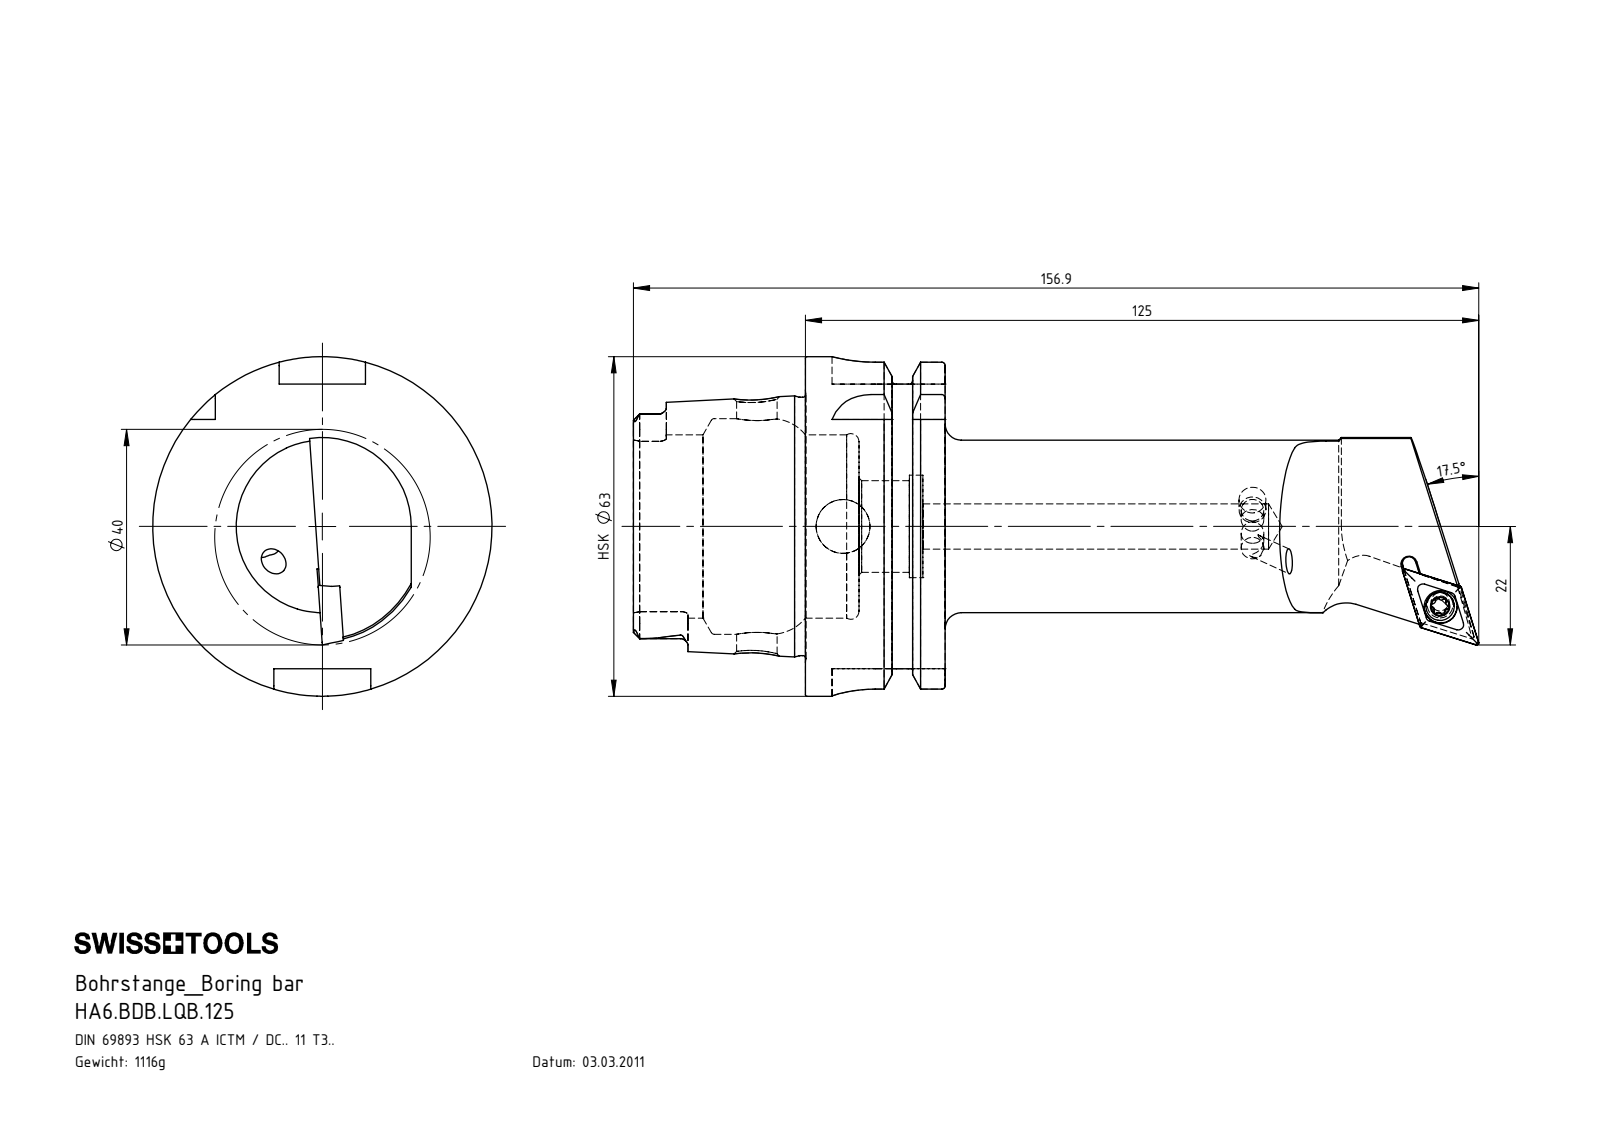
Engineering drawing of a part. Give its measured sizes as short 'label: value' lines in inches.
name: WCB-ER2.001.009_A; DCMT11T304; HA6.BDB.LQB.125; HA6-BDB.LQB.125_B (+1 more)
written by: SolidWorks 2017 (AUTOMOTIVE_DESIGN)
unit: in
bodies: 5 solids, 310 faces (79 planar, 91 cylindrical, 140 other)
size: 6.177 × 2.48 × 2.48
volume: 8.718 in³; area: 53.05 in²
holes: 2× ⌀0.165, 1× ⌀0.13, 1× ⌀0.157, 1× ⌀0.173, 1× ⌀0.197, 1× ⌀0.24, 1× ⌀0.295, 1× ⌀0.331, 1× ⌀0.394, 1× ⌀0.669, 1× ⌀0.748, 1× ⌀1.339
bosses: 1× ⌀2.48, 1× ⌀2.163, 1× ⌀1.887, 1× ⌀1.26, 1× ⌀0.207, 1× ⌀0.197, 1× ⌀0.157
rounds: 6× R0.013, 6× R0.023, 6× R0.055, 4× R0.315, 2× R0.111, 2× R0.113, 1× R0.049, 1× R0.118
face distances: 1.022, 0.63, 0.392, 1.256, 1.648, 2.278, 2.079, 0.858, 0.467, 2.114
